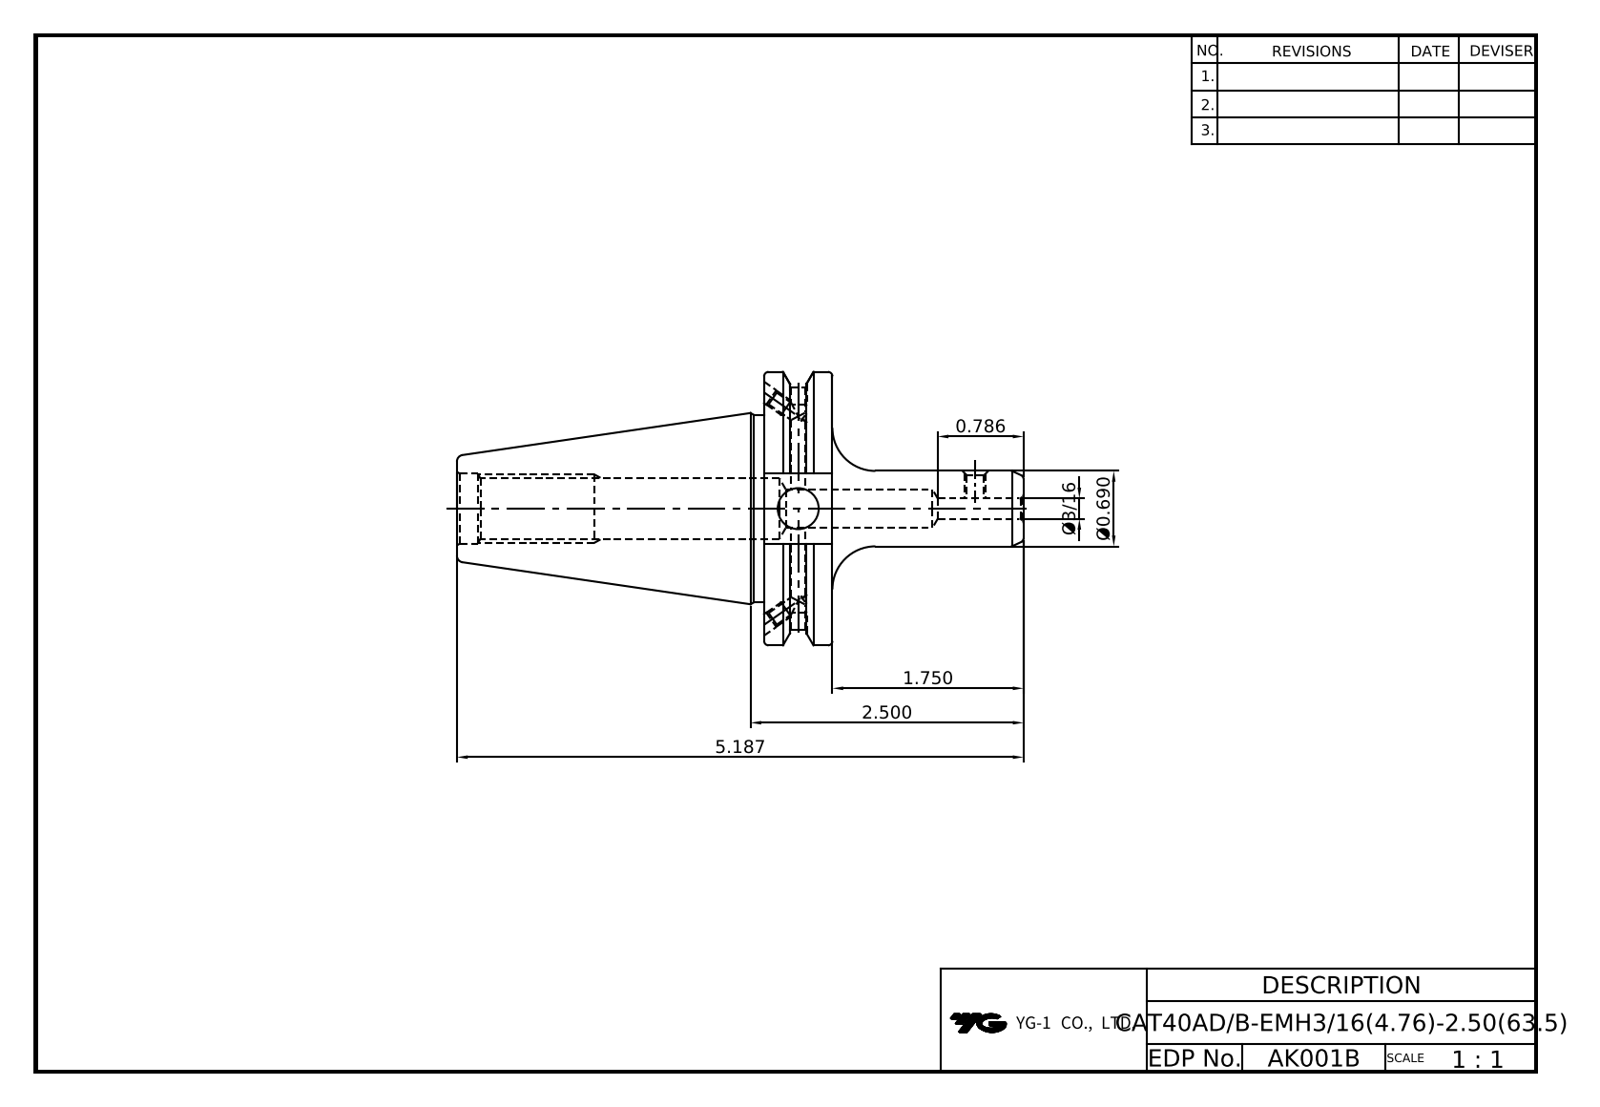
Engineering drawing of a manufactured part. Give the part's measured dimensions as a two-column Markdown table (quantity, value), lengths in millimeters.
| quantity | value |
| --- | --- |
| part name | LO-CAT40ADB-EMH4.7625-63.5 |
| STEP written by | Autodesk Inventor 2025 (AUTOMOTIVE_DESIGN) |
| units | millimeters |
| bodies | 1 solid, 87 faces (35 planar, 28 cylindrical, 24 other) |
| overall size | 131.75 × 63.5 × 61.09 |
| volume | 110 900 mm³ |
| surface area | 24 194 mm² |
| round holes (diameter × count) | 3.24 × 4, 4 × 2, 4.2 × 2, 3.96 × 1, 4.76 × 1, 9 × 1, 9.53 × 1, 13.39 × 1, 16.3 × 1 |
| round bosses / shafts (diameter × count) | 63.5 × 1, 43.6 × 1, 17.53 × 1 |
| partial cylindrical surfaces (radius × count) | 28.15 × 1 |
| main face-to-face distances | 15.88, 47.6, 16.38, 71.42, 87.3, 77.47, 6.05, 9.83, 81.3, 9.88 |
